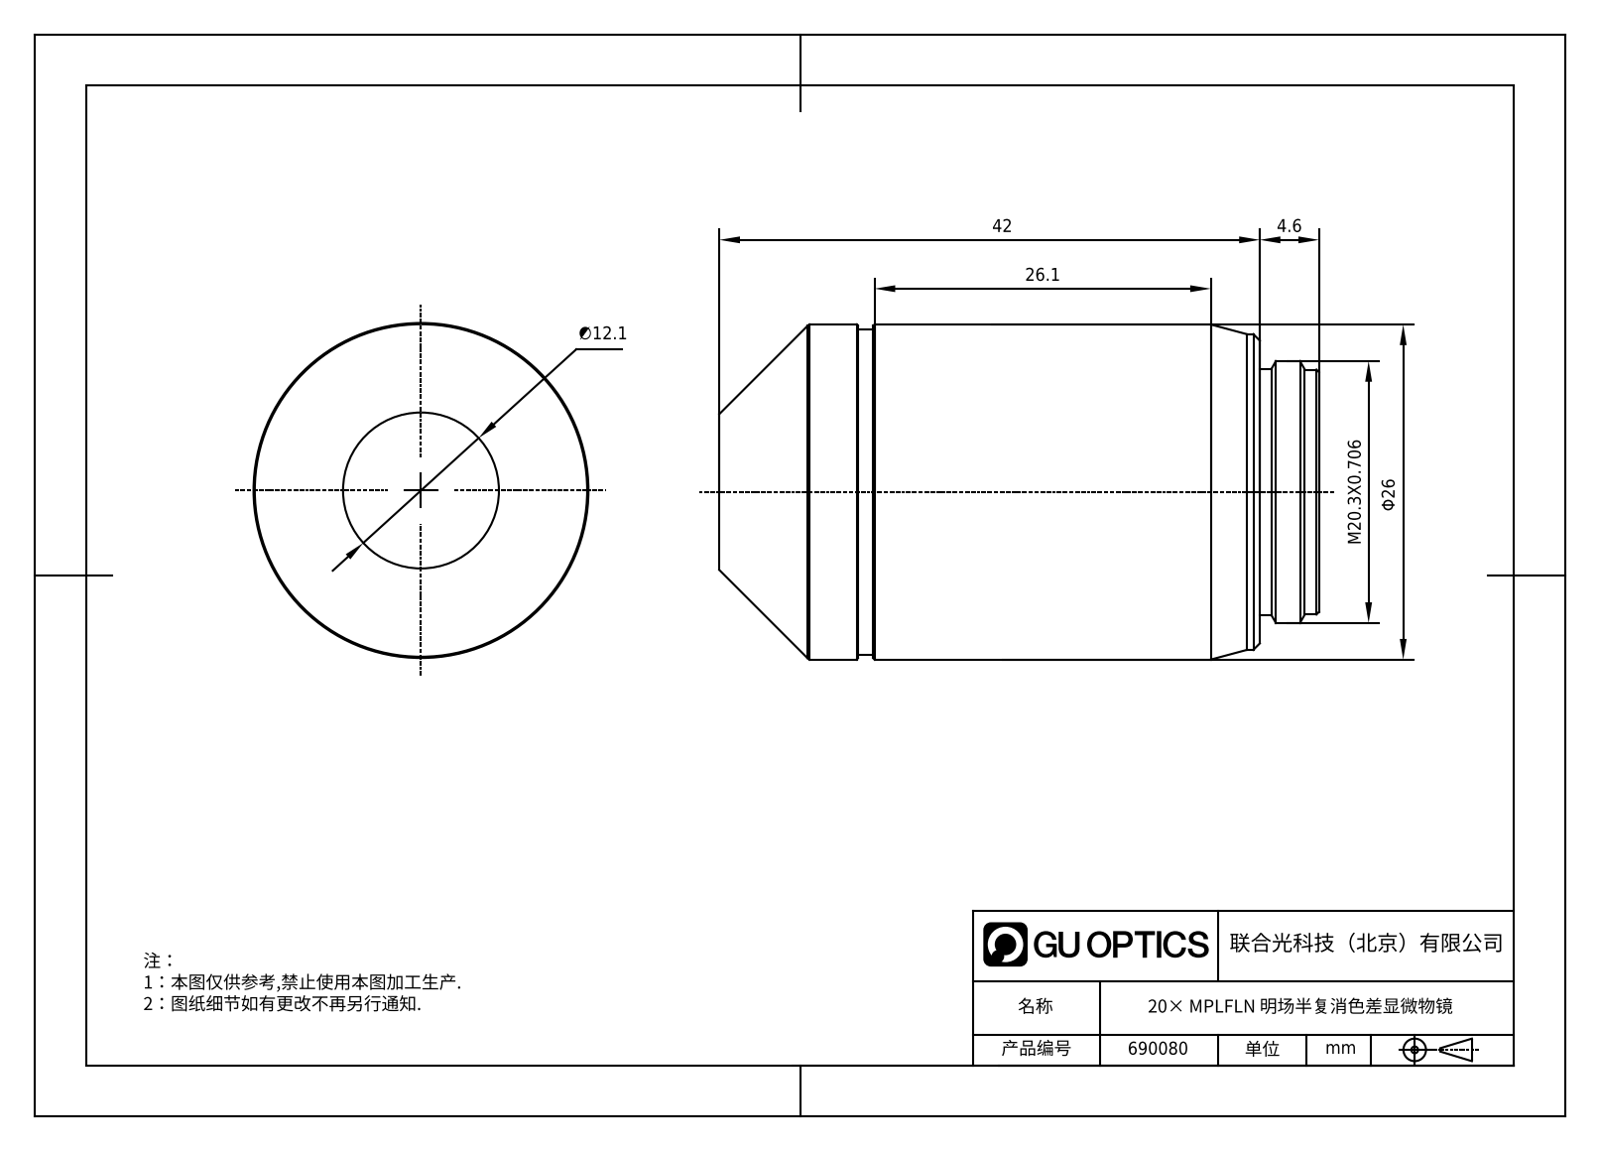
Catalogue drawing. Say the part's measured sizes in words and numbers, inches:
The part is named "MPLFLN20X.stp; 690080; 690080.stp". Its 3-D file was written by "SolidWorks 2020 (CONFIG_CONTROL_DESIGN)". It is 1 solid with 37 faces: 5 planar, 14 cylindrical and 18 other. Overall it measures 1.833 by 1.024 by 1.024 inches. Its volume is 1.334 cubic inches and its surface area 6.784 square inches. Round bosses or shafts: 1 of diameter 1.024, 1 of diameter 0.992, 1 of diameter 0.965, 1 of diameter 0.8, 1 of diameter 0.752, 1 of diameter 0.748. The main face-to-face distances are 0.181, 1.652, 1.833, 0.423, 0.47, 0.047, 1.228, 1.409, 1.181, 1.362.
